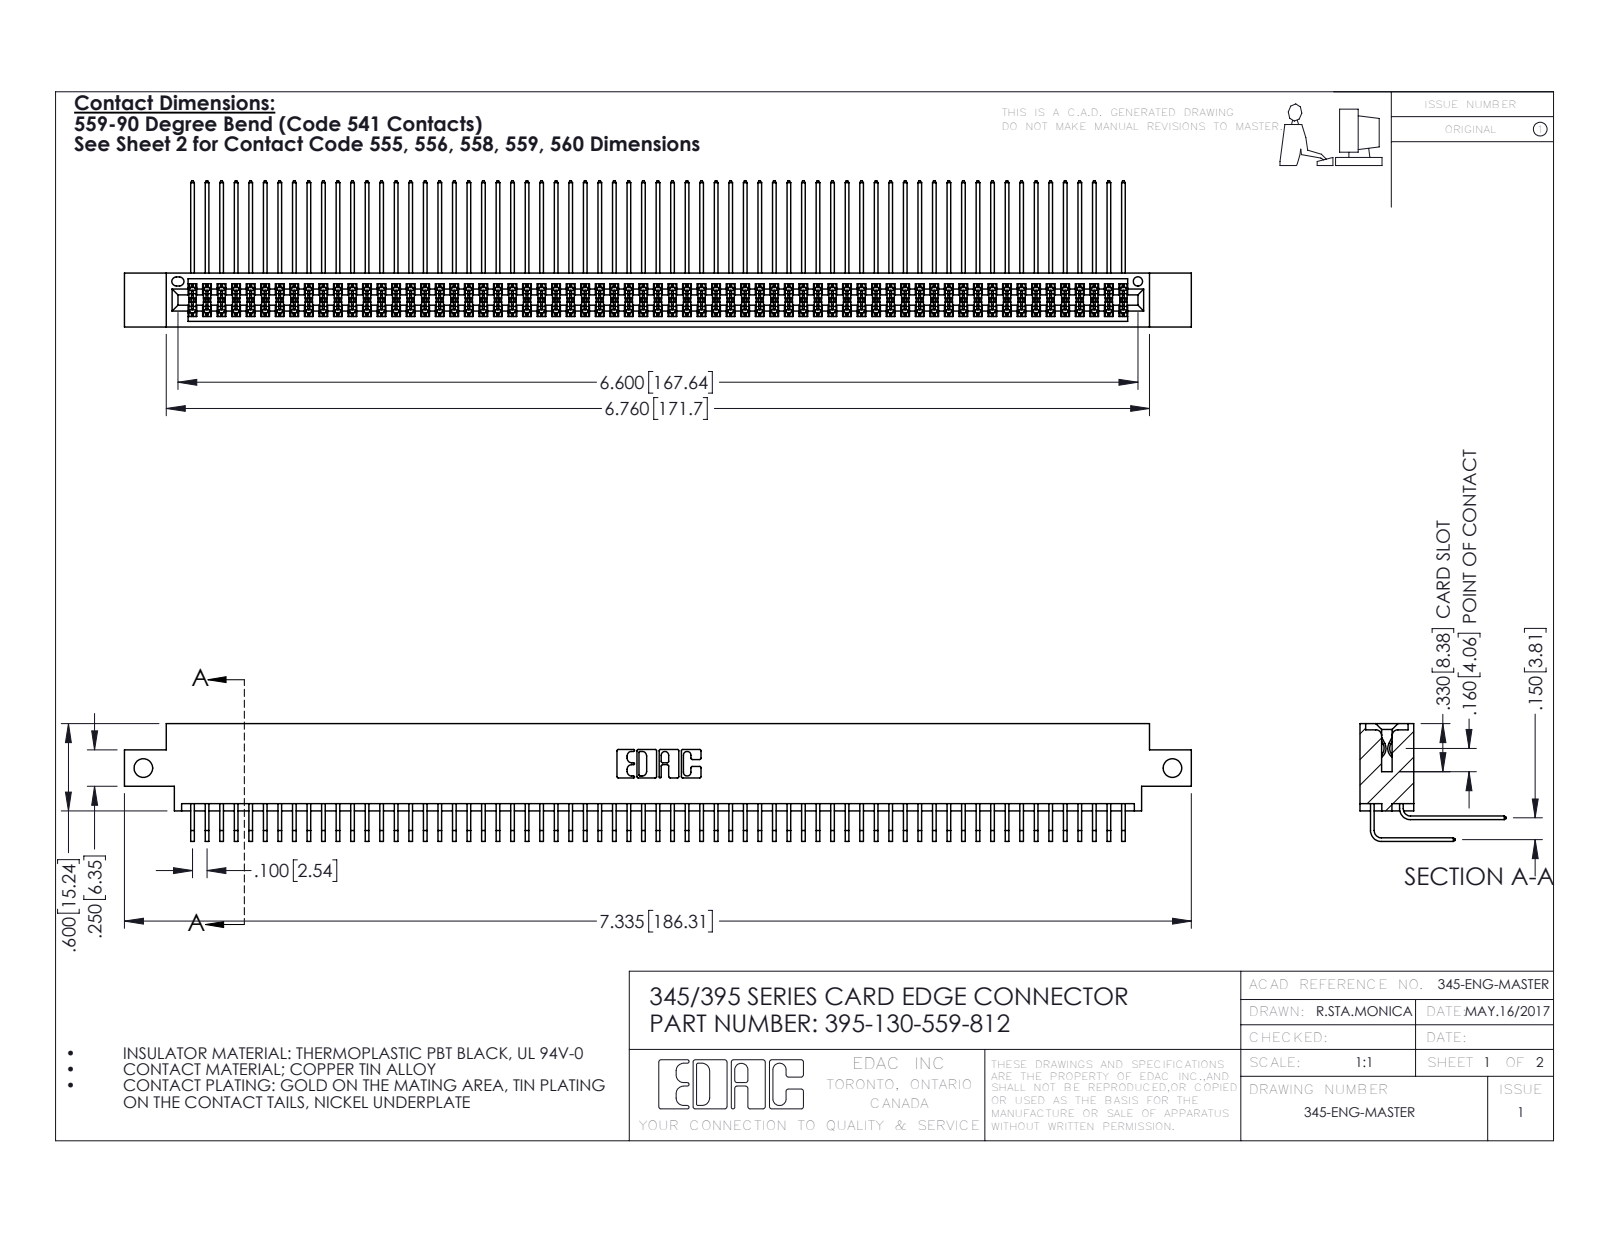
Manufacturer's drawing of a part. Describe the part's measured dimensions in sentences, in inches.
The part is named "345-292-001_559 Tail - 2; 345-292-001_558 559 Tail - 1; 345 Part_0.170 Offset - Side Mount; 395-130-559-812". Its 3-D file was written by "SolidWorks 2016 (CONFIG_CONTROL_DESIGN)". It is 131 solids with 6890 faces: 4634 planar, 2256 cylindrical and 0 other. Overall it measures 7.335 by 1.005 by 0.809 inches. Its volume is 1.151 cubic inches and its surface area 49.38 square inches. Round holes: 2 of diameter 0.128, 1 of diameter 0.064. Partial cylindrical surfaces (rounded edges, fillets, slot ends): 196 of radius 0.006, 22 of radius 0.01, 6 of radius 0.007, 6 of radius 0.031, 3 of radius 0.026, 2 of radius 0.014, 2 of radius 0.019, 2 of radius 0.022. The main face-to-face distances are 0.072, 0.298, 0.37, 0.2, 0.098, 0.272, 0.025, 0.225, 0.175, 0.15. The hole center spacings are 7.075.
